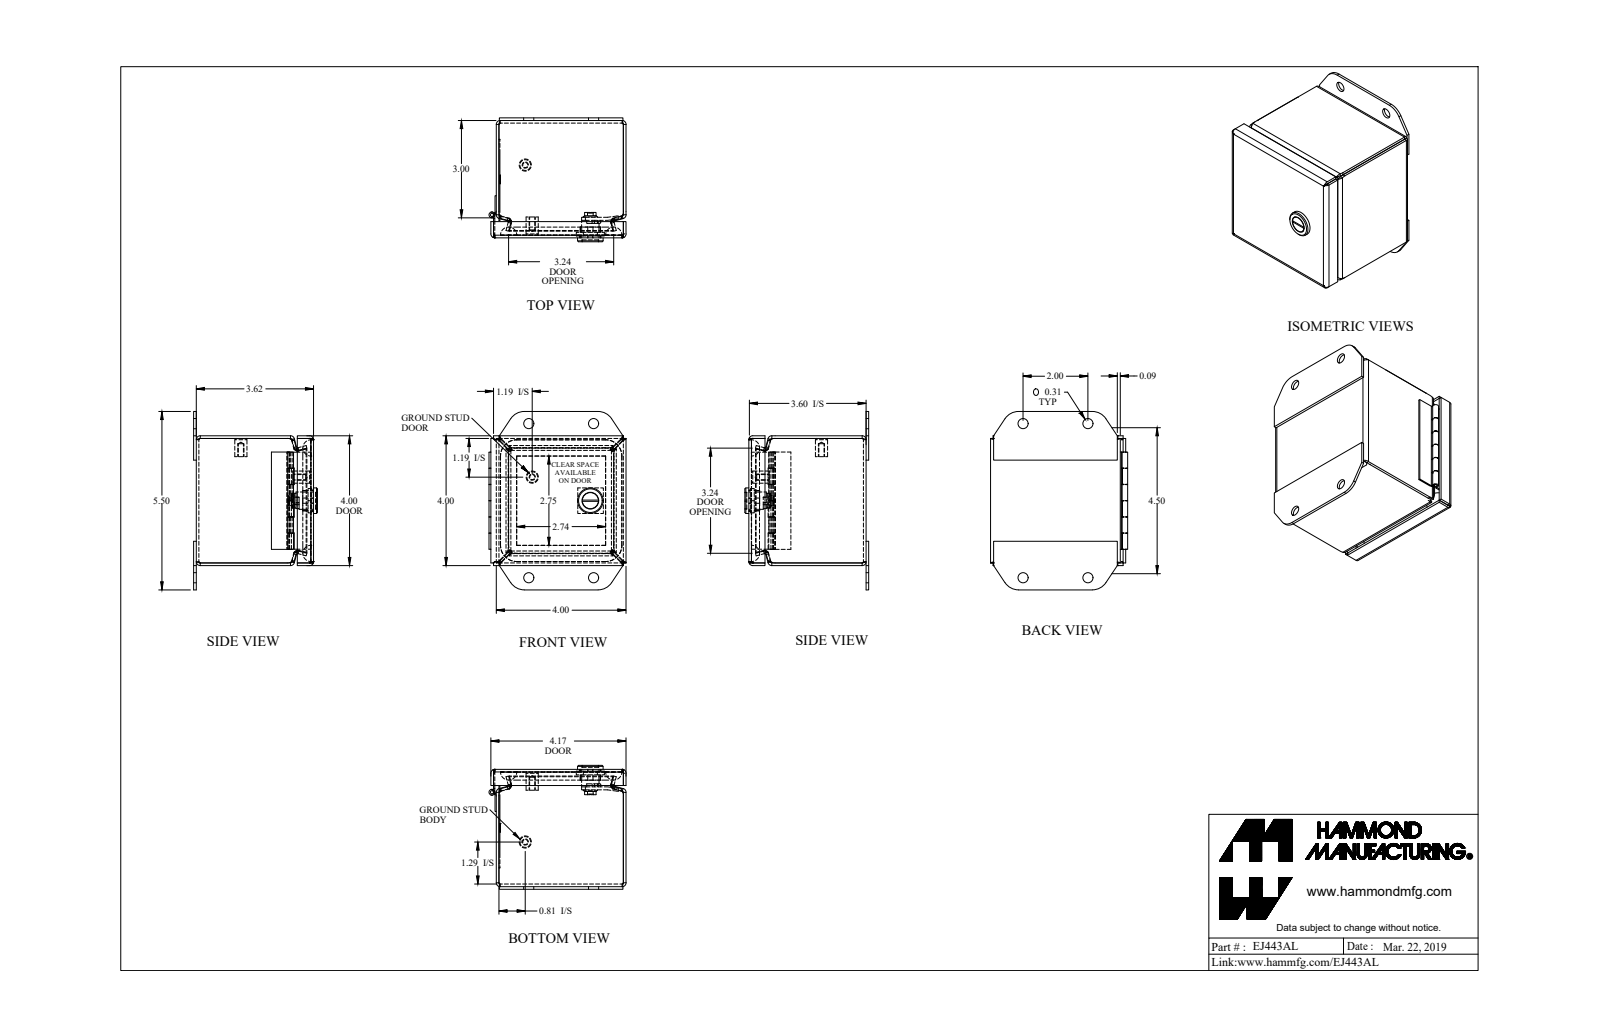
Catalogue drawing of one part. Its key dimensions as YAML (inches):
part_name: "EJ443AL_Default"
step_written_by: "SolidWorks 2019 (CONFIG_CONTROL_DESIGN)"
units: inches
bodies: {solids: 9, faces: 456, planar: 278, cylindrical: 118, other: 60}
overall_size: [5.5, 4.226, 3.82]
volume: 10.02
surface_area: 254.4
round_holes:
  - {diameter: 0.313, count: 4}
  - {diameter: 0.159, count: 2}
  - {diameter: 0.516, count: 1}
round_bosses_or_shafts:
  - {diameter: 0.375, count: 2}
  - {diameter: 0.33, count: 2}
  - {diameter: 0.788, count: 1}
  - {diameter: 0.535, count: 1}
  - {diameter: 0.496, count: 1}
  - {diameter: 0.435, count: 1}
  - {diameter: 0.18, count: 1}
  - {diameter: 0.1, count: 1}
partial_cylinders:
  - {radius: 0.041, count: 16}
  - {radius: 0.121, count: 16}
  - {radius: 0.281, count: 12}
  - {radius: 0.25, count: 4}
  - {radius: 0.499, count: 4}
  - {radius: 0.5, count: 4}
  - {radius: 0.06, count: 2}
  - {radius: 0.03, count: 1}
face_to_face_distances: [0.081, 3.919, 3.536, 3.617, 4, 3.838, 3.455, 3.698, 0.162, 0.082]
hole_center_spacings: [2, 2.377, 3.041, 4.75, 5.154, 1.652, 1.934, 2.51]
